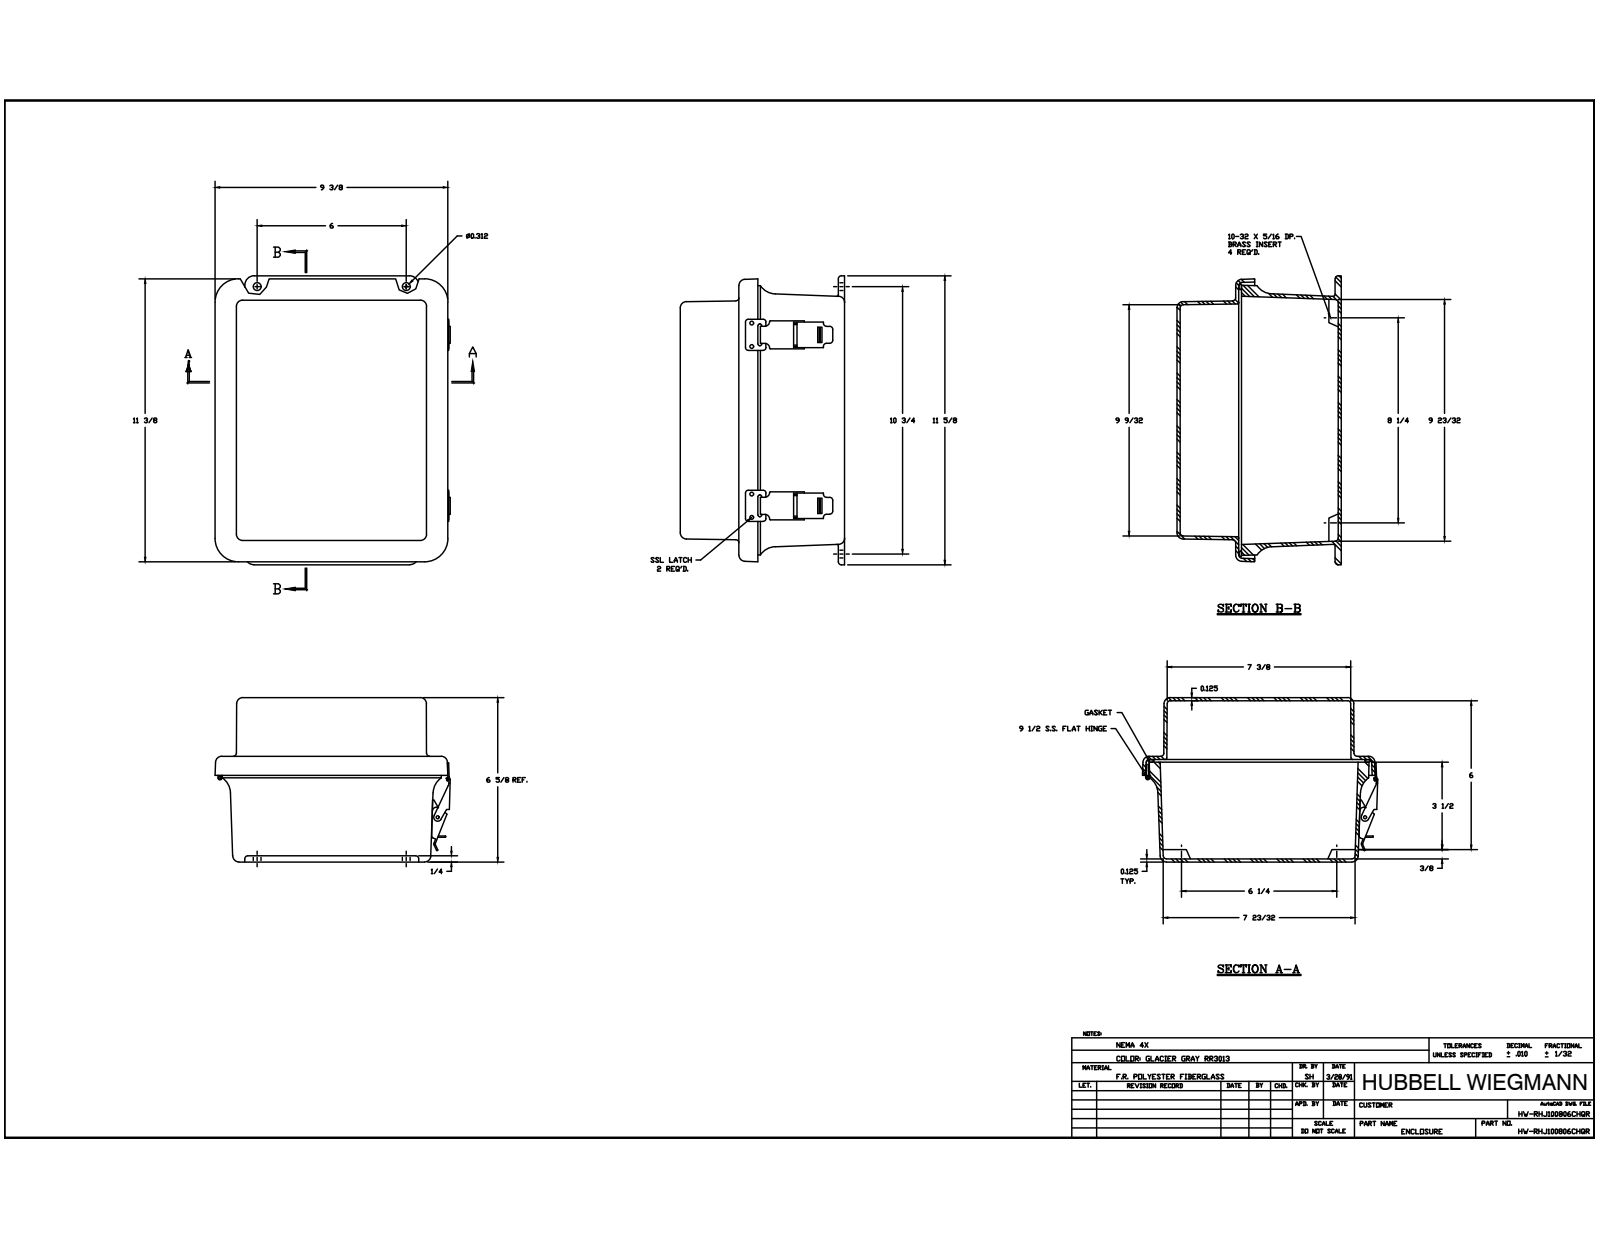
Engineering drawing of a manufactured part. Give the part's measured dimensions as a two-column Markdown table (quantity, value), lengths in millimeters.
| quantity | value |
| --- | --- |
| part name | J1008HL_9; RMINS45821P_129; RMINS45821P_130; RMINS45821P_131 (+8 more) |
| STEP written by | Autodesk Inventor 2014 (AUTOMOTIVE_DESIGN) |
| units | millimeters |
| bodies | 38 solids, 989 faces (409 planar, 409 cylindrical, 171 other) |
| overall size | 295.27 × 242.16 × 167.48 |
| volume | 1 132 000 mm³ |
| surface area | 636 573 mm² |
| round holes (diameter × count) | 3.56 × 20, 2.64 × 8, 3.33 × 8, 3.86 × 5, 3.3 × 4, 3.96 × 4, 5.54 × 4, 3.43 × 2, 9.52 × 2, 2.16 × 1, 2.16 × 1 |
| round bosses / shafts (diameter × count) | 3.17 × 16, 6.35 × 8, 6.86 × 4, 7.62 × 1, 4.31 × 1, 3.94 × 1, 3.05 × 1 |
| partial cylindrical surfaces (radius × count) | 3.17 × 32, 0.38 × 20, 0.79 × 20, 1.14 × 16, 0.76 × 12, 6.35 × 12, 0.57 × 9, 1.52 × 6 |
| main face-to-face distances | 3.17, 3.18, 161.13, 164.3, 167.48, 164.31, 104.36, 101.19, 59.94, 63.12 |
| hole center spacings | 177.8, 178.82, 23.81, 152.4, 19.05, 76.2, 6.35, 19.04 |
